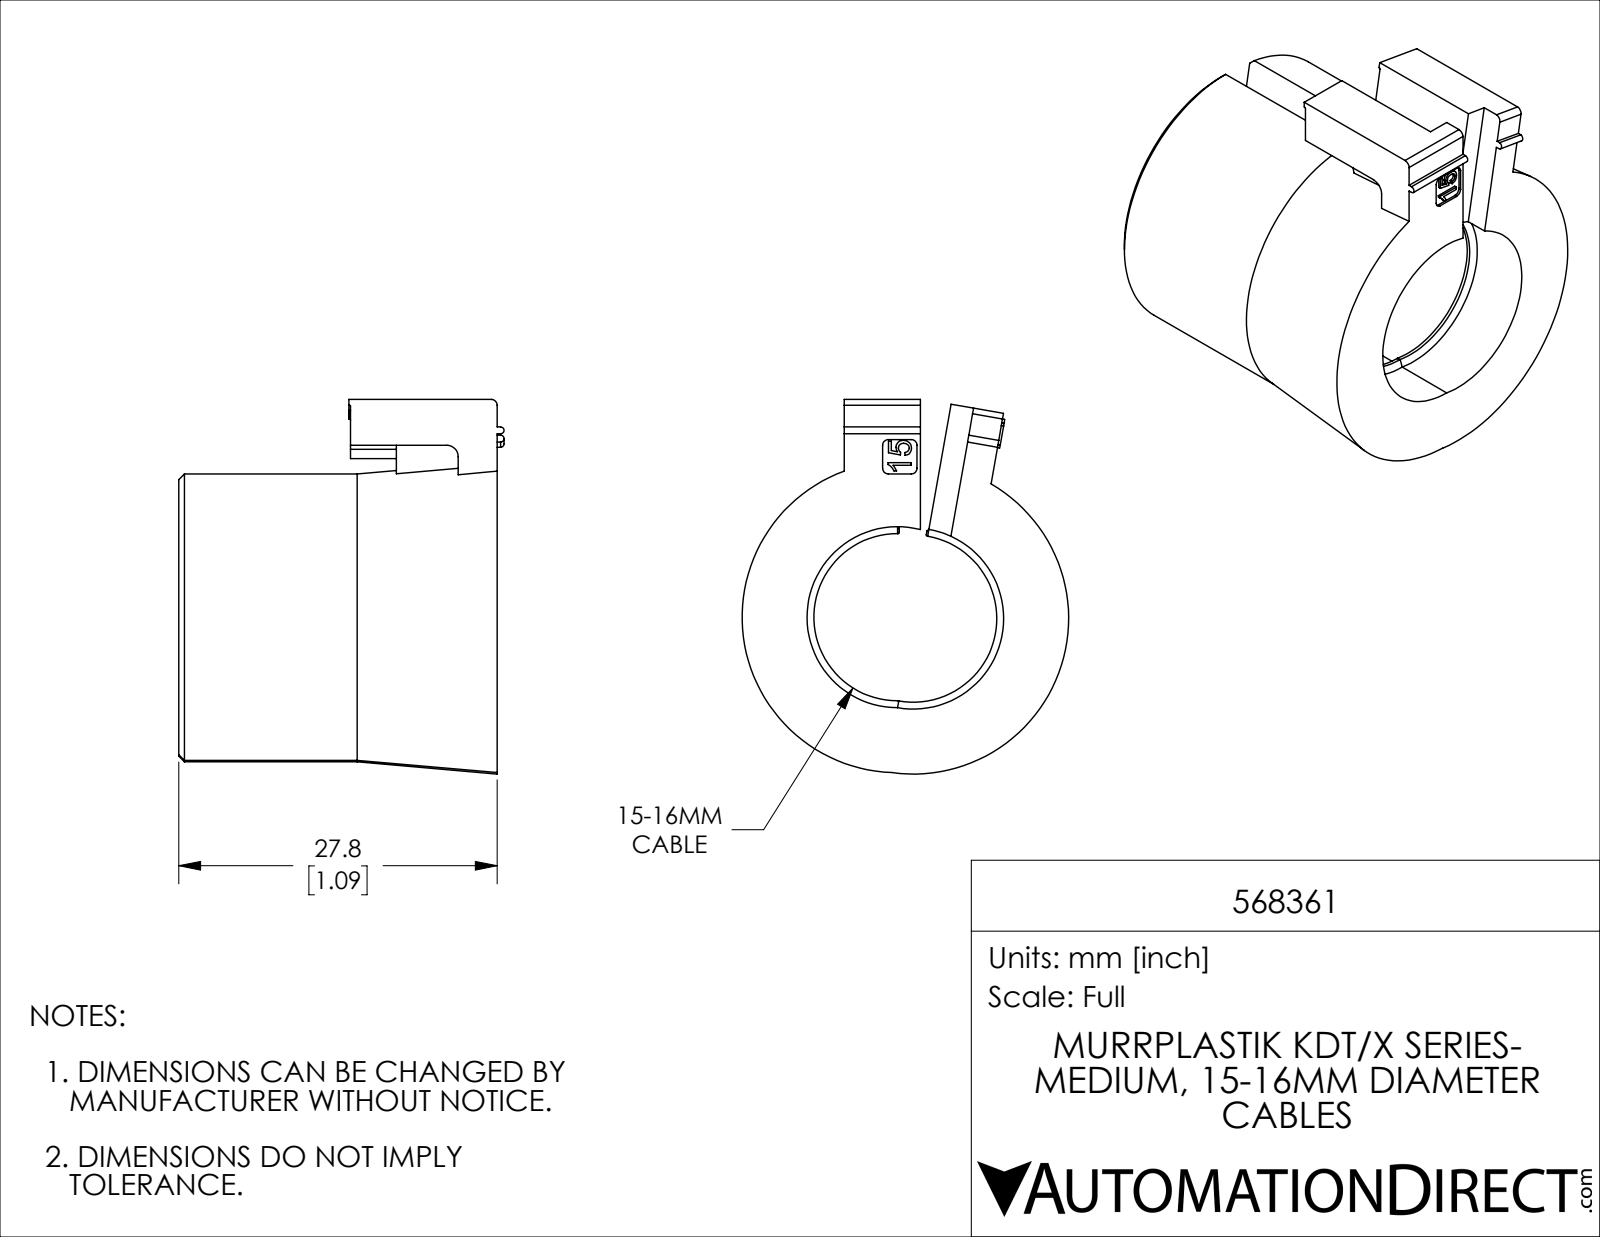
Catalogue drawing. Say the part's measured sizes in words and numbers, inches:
The part is named "568361". Its 3-D file was written by "SolidWorks 2019 (CONFIG_CONTROL_DESIGN)". It is 1 solid with 124 faces: 73 planar, 28 cylindrical and 23 other. Overall it measures 1.287 by 1.123 by 1.118 inches. Its volume is 0.566 cubic inches and its surface area 7.901 square inches. Partial cylindrical surfaces (rounded edges, fillets, slot ends): 6 of radius 0.004, 6 of radius 0.02, 2 of radius 0.012, 2 of radius 0.039, 2 of radius 0.287, 2 of radius 0.311, 2 of radius 0.492. The main face-to-face distances are 1.094, 0.079, 0.183, 0.183, 1.016, 0.157, 0.504, 0.425, 0.591, 0.158.
